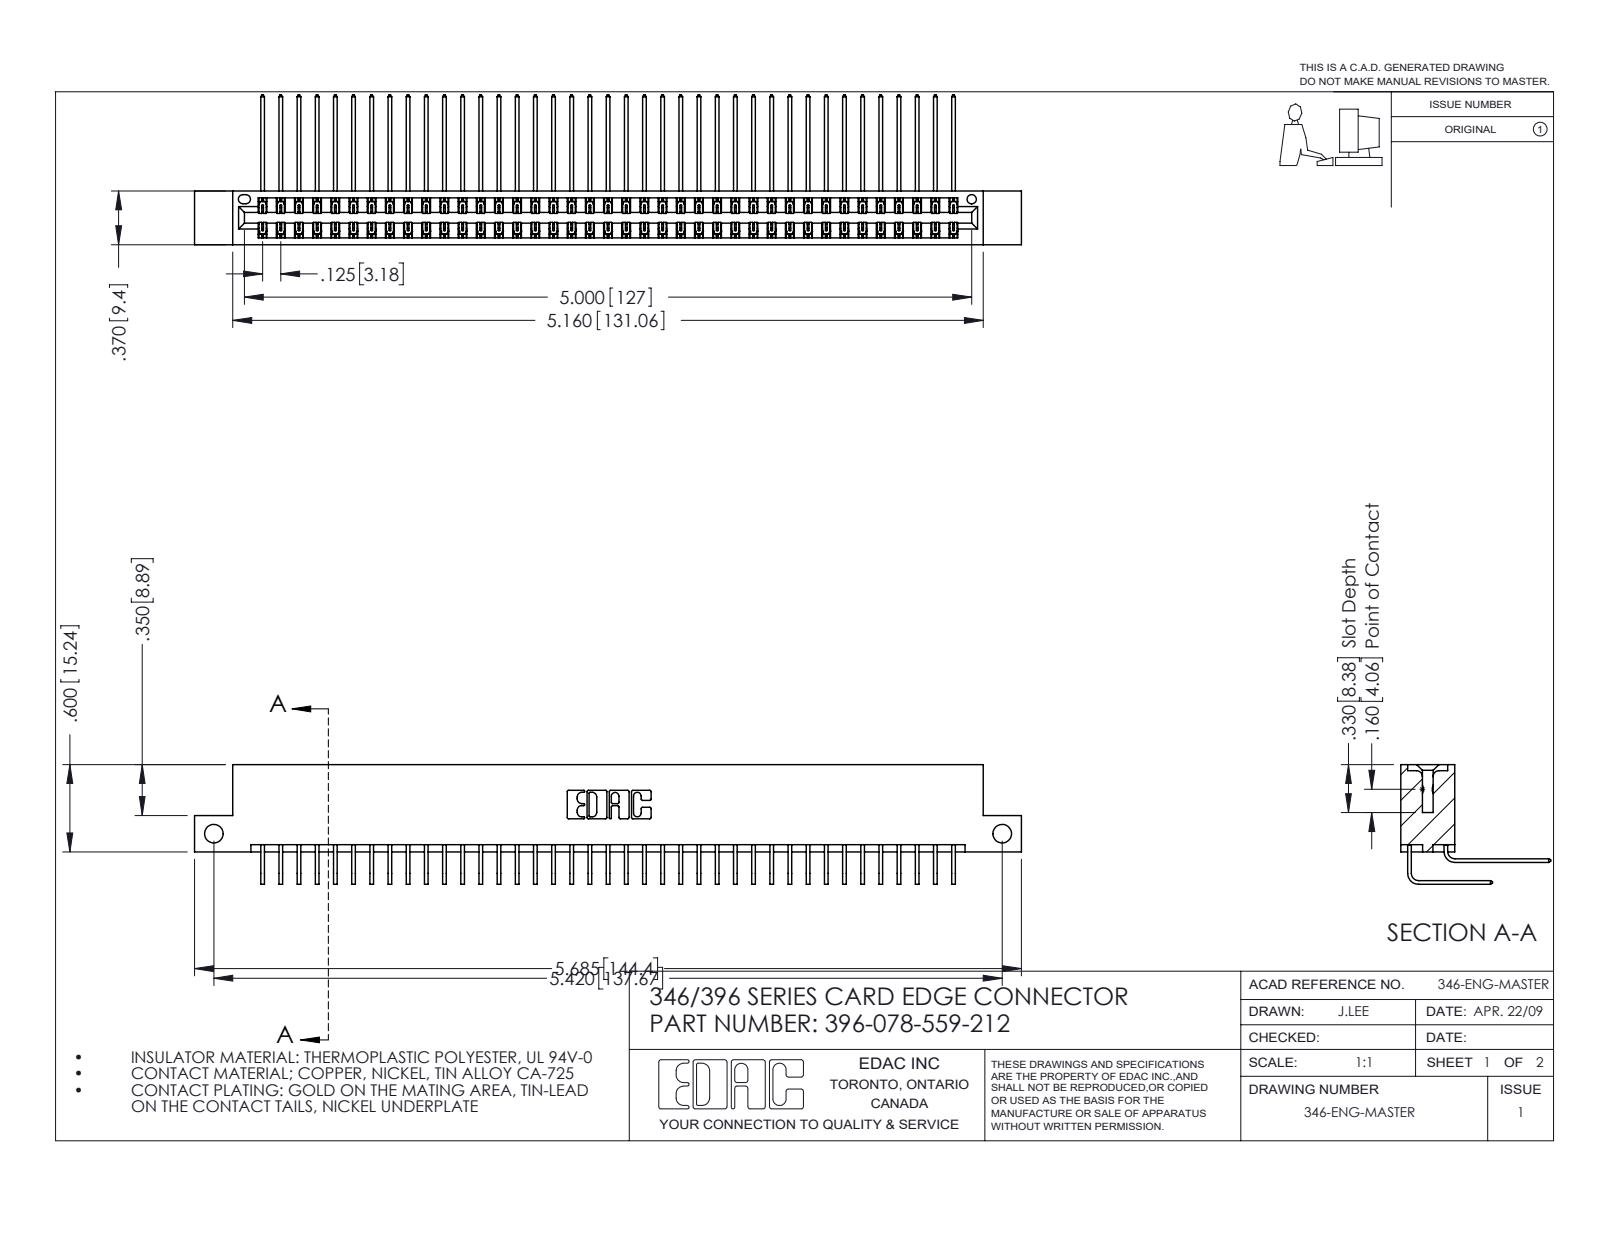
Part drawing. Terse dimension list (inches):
name: 345-292-001_558 559 Tail - 1; 346 Part_Flush Mounting Lugs - Side Mount; 396-078-559-212; 345-292-001_559 Tail - 2
written by: SolidWorks 2016 (CONFIG_CONTROL_DESIGN)
unit: in
bodies: 79 solids, 4334 faces (2962 planar, 1372 cylindrical, 0 other)
size: 5.685 × 1.03 × 0.823
volume: 0.88 in³; area: 33.78 in²
holes: 2× ⌀0.128, 1× ⌀0.064
rounds: 117× R0.006, 22× R0.01, 6× R0.007, 6× R0.031, 3× R0.026, 2× R0.014, 2× R0.022, 2× R0.024
face distances: 0.048, 0.322, 0.025, 0.37, 0.25, 0.072, 0.298, 0.275, 0.148, 0.222
hole spacings: 5.42
